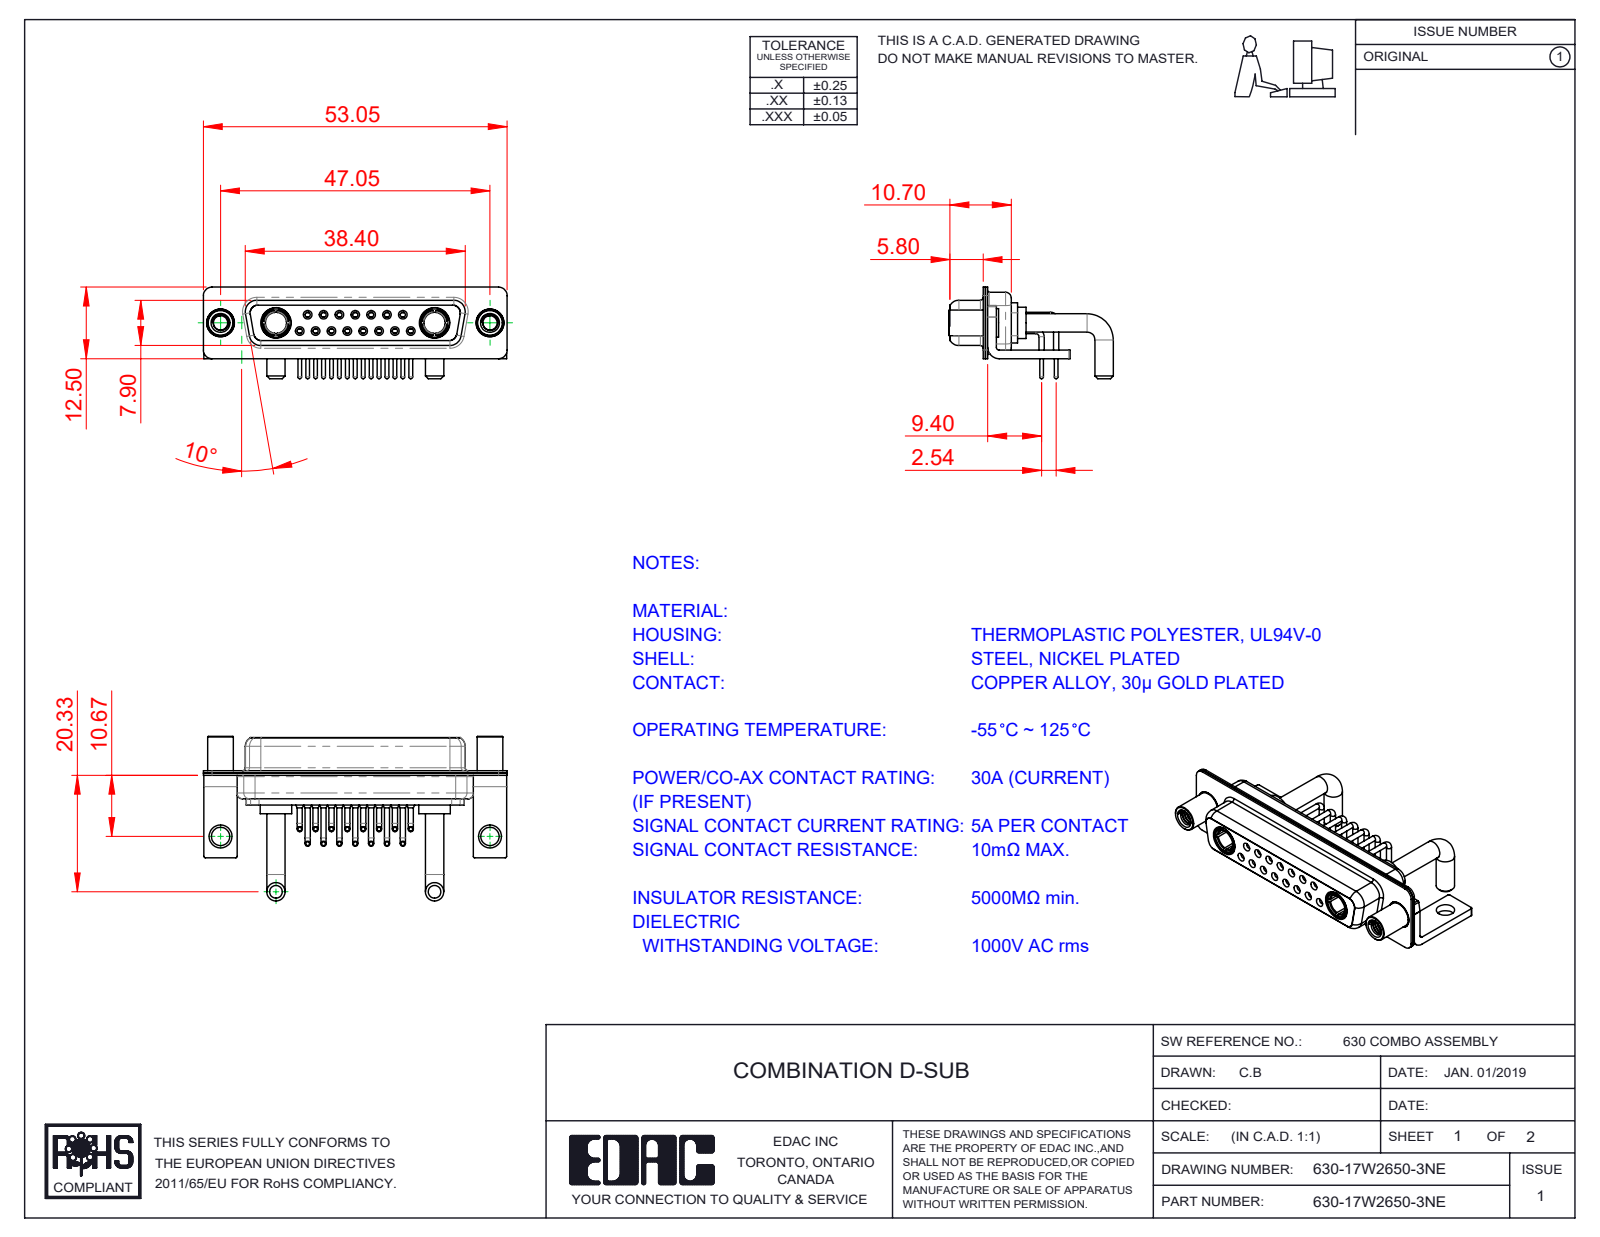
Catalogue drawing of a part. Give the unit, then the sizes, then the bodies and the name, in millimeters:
Units: millimetres
Overall size (bounding box): 53.05 × 28.73 × 16
Round holes (diameter × count): ⌀0.9 ×15, ⌀1.1 ×15, ⌀1.5 ×15, ⌀2 ×15, ⌀1.6 ×8, ⌀1.7 ×7, ⌀4.85 ×4, ⌀2.5 ×2, ⌀3.2 ×2, ⌀3.7 ×2, ⌀4 ×2, ⌀4.05 ×2
Round bosses / shafts (diameter × count): ⌀0.9 ×15, ⌀0.65 ×15, ⌀1.6 ×7, ⌀3.2 ×4, ⌀5.5 ×2, ⌀5.2 ×2, ⌀5 ×2, ⌀4.96 ×2
Partial cylindrical surfaces — rounded edges, fillets, slot ends (radius × count): R0.25 ×16, R1.5 ×16, R2 ×13, R1.35 ×8, R1.6 ×8, R0.5 ×5, R0.6 ×4, R0.65 ×4
Main face-to-face distances: 0.4, 0.45, 1.4, 8.45, 1.8, 0.8, 8.9, 6.2, 7.05, 1.5
Hole centre spacings: 3.16, 2.77, 5.54, 8.31, 5.04, 7.49, 11.08, 5.03
Volume: 4 579 mm³ · Surface area: 10 281 mm²
Bodies: 26 solids, 1328 faces (372 planar, 604 cylindrical, 352 other)
Part name (STEP PRODUCT): 630Combo Housing_17W2; Power Socket_Ext 30A RA; 630Combo Stabilizer Bracket; 630Combo Shell Front_25 Contacts (+5 more)
STEP written by: SolidWorks 2020 (CONFIG_CONTROL_DESIGN)
